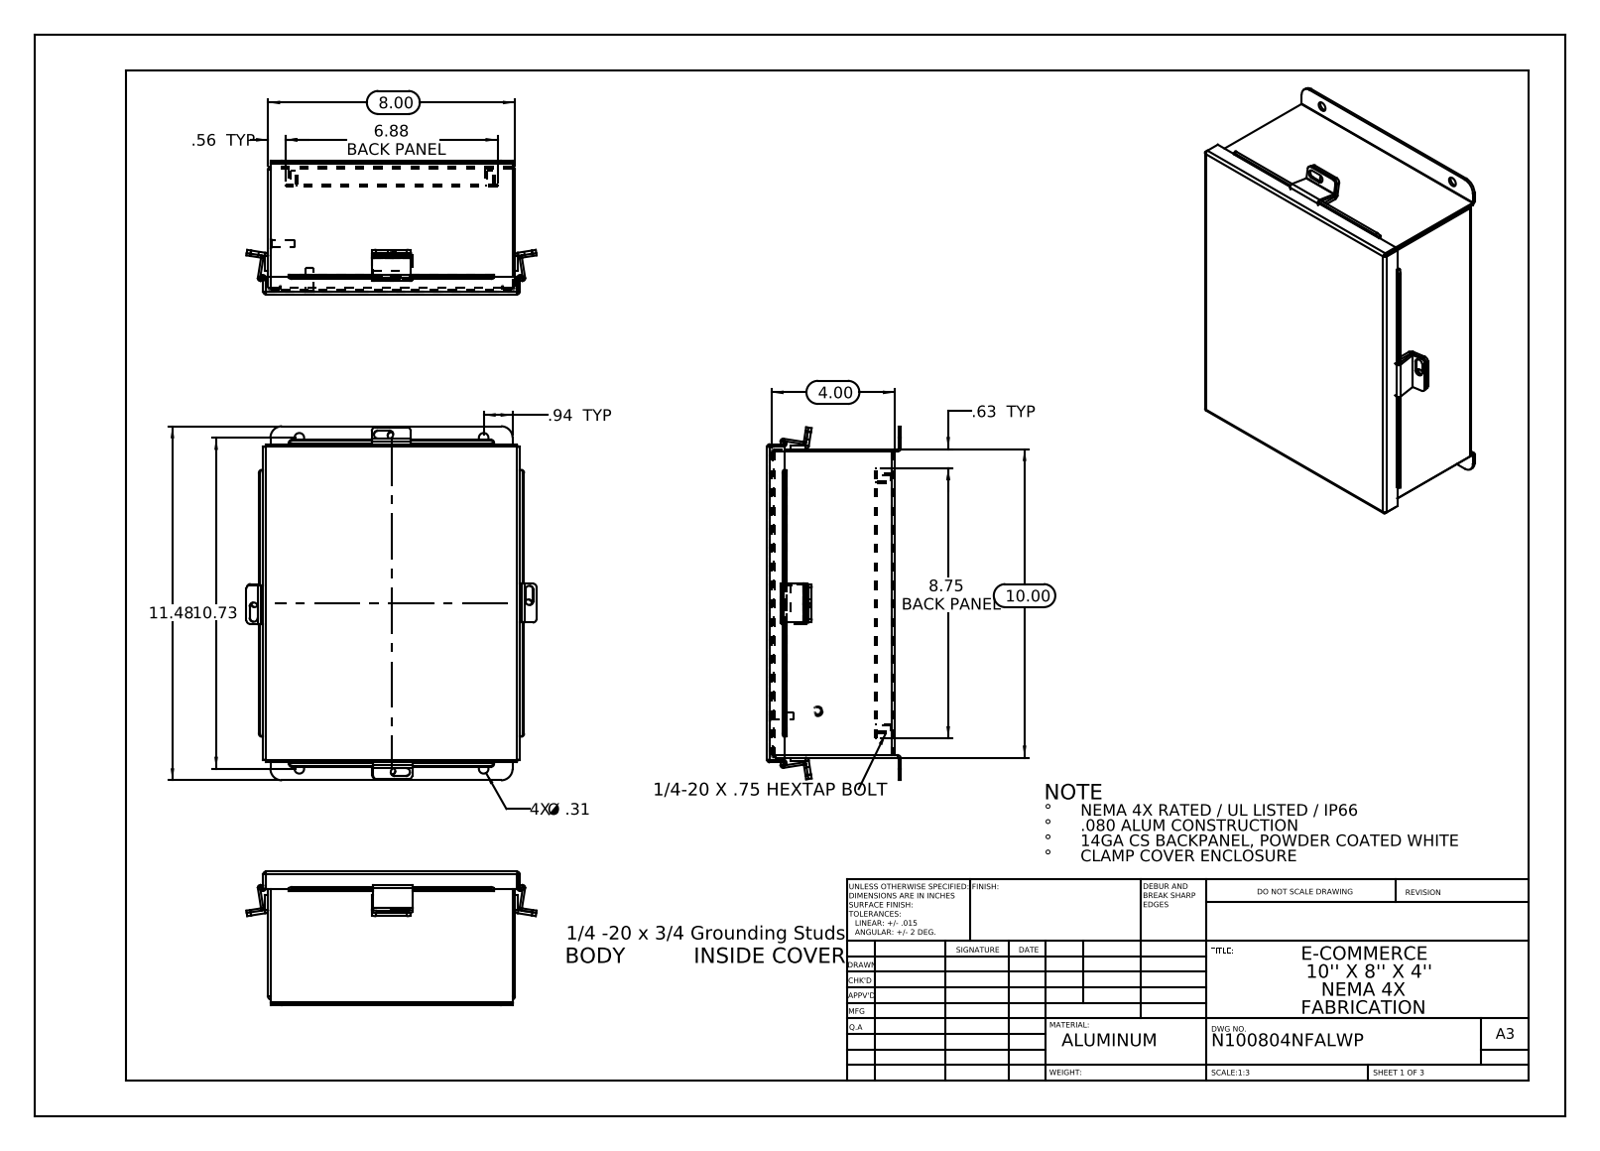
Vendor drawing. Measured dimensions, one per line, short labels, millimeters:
name: N100804NFSSWP JIC Cover Clamp; N100804NFSSWP JIC Bottom; N100804NFSSWP HW-CD-S-25020-034; N100804NFSSWP JIC Top (+6 more)
written by: SolidWorks 2013 (CONFIG_CONTROL_DESIGN)
unit: mm
bodies: 19 solids, 456 faces (292 planar, 144 cylindrical, 20 other)
size: 291.5 × 238.9 × 111.5
volume: 522 100 mm³; area: 559 500 mm²
holes: 8× ⌀6.4, 4× ⌀4.7, 4× ⌀7.9
bosses: 4× ⌀8, 2× ⌀8, 2× ⌀6
rounds: 16× R0.2, 14× R3.2, 12× R0.3, 12× R2.2, 8× R2.1, 8× R2.5, 8× R3.4, 4× R2.1
face distances: 1.9, 104.9, 102.9, 106.8, 201.3, 252.1, 1.9, 88.4, 14.6, 12.7
hole spacings: 33.4, 160.3, 239.5, 286.2, 151.8, 161.9, 206.4, 262.3
